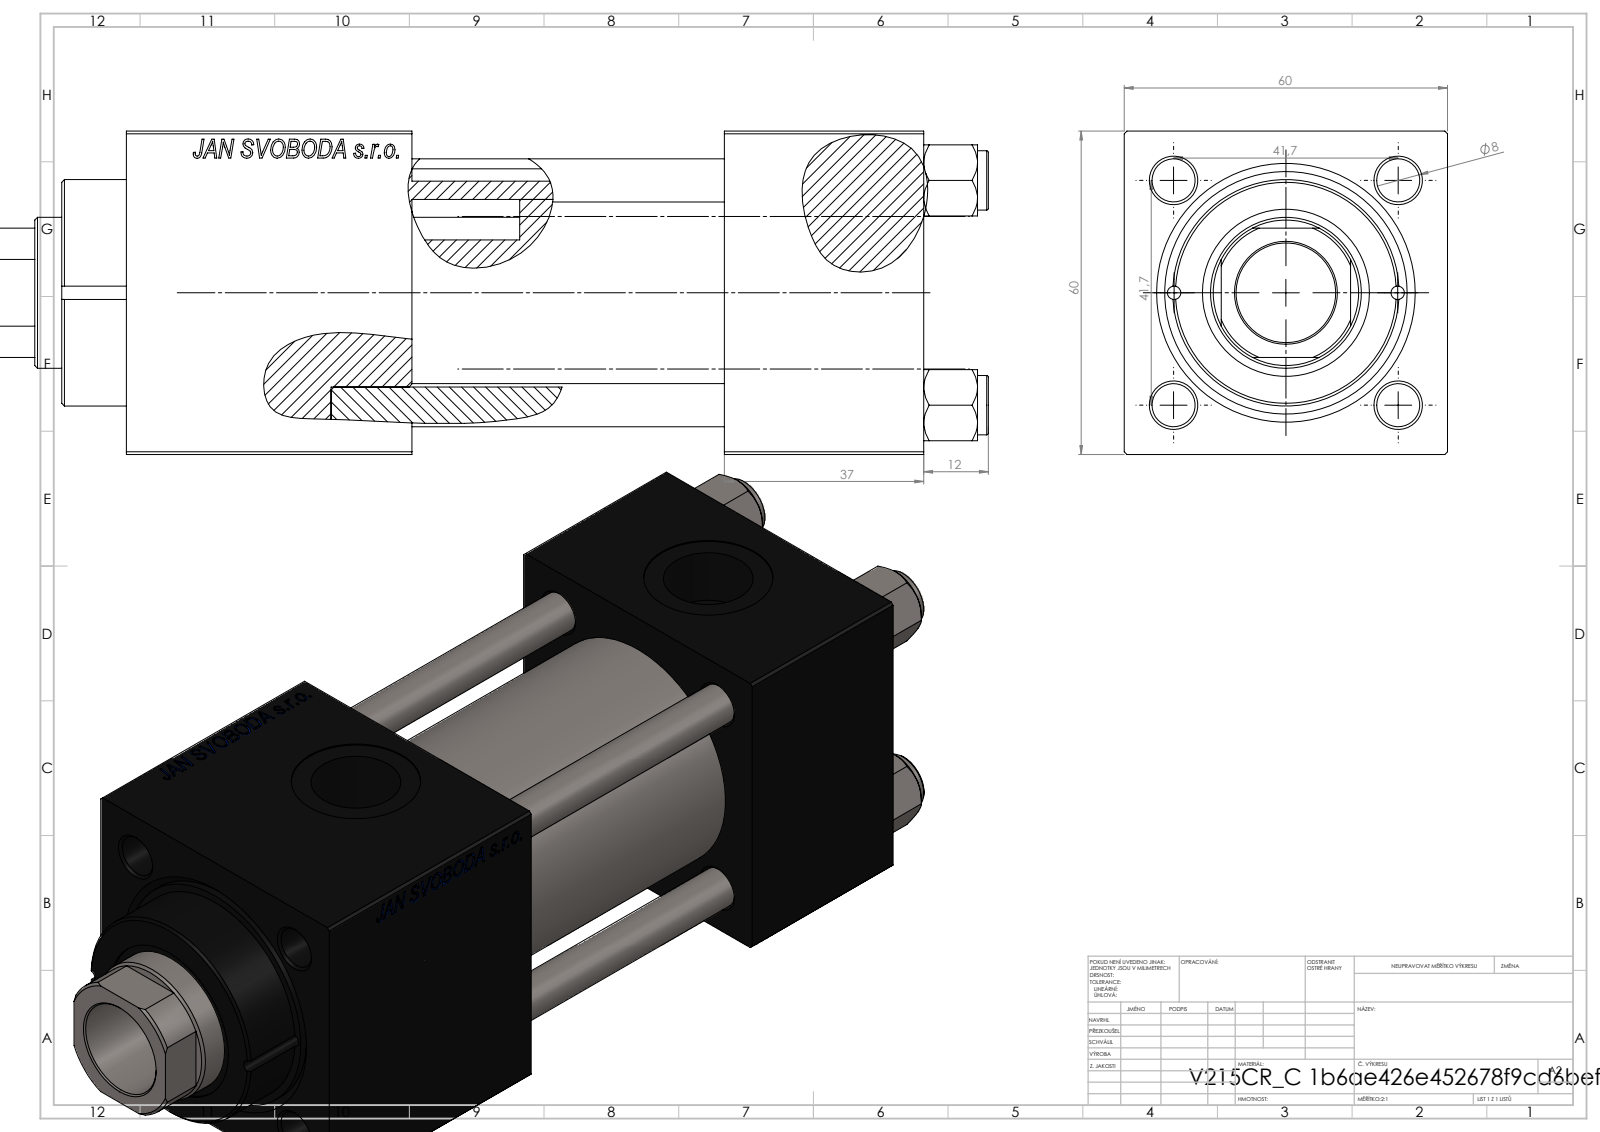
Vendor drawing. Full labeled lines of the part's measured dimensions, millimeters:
Part name (STEP PRODUCT): NUT_M5_C; V215_VC_A; V215CR_VCP_C; V215CR_C_Body (+1 more)
STEP written by: SolidWorks 2019 (CONFIG_CONTROL_DESIGN)
Units: millimetres
Bodies: 11 solids, 1155 faces (528 planar, 91 cylindrical, 536 other)
Overall size (bounding box): 185 × 60 × 60
Volume: 423 965 mm³ · Surface area: 111 559 mm²
Round holes (diameter × count): ⌀8 ×4, ⌀2.5 ×2, ⌀7 ×2, ⌀16.66 ×2, ⌀24 ×2, ⌀18.5 ×1, ⌀28 ×1, ⌀31 ×1, ⌀40 ×1, ⌀45 ×1
Round bosses / shafts (diameter × count): ⌀11 ×4, ⌀46 ×1, ⌀42 ×1
Partial cylindrical surfaces — rounded edges, fillets, slot ends (radius × count): R13.5 ×1
Main face-to-face distances: 60, 37, 58, 95, 53, 119.3, 82.3, 24.3, 148, 111
Hole centre spacings: 20.85, 29.49, 41.7, 46.53, 20.75, 58.97, 41.5, 92.5
